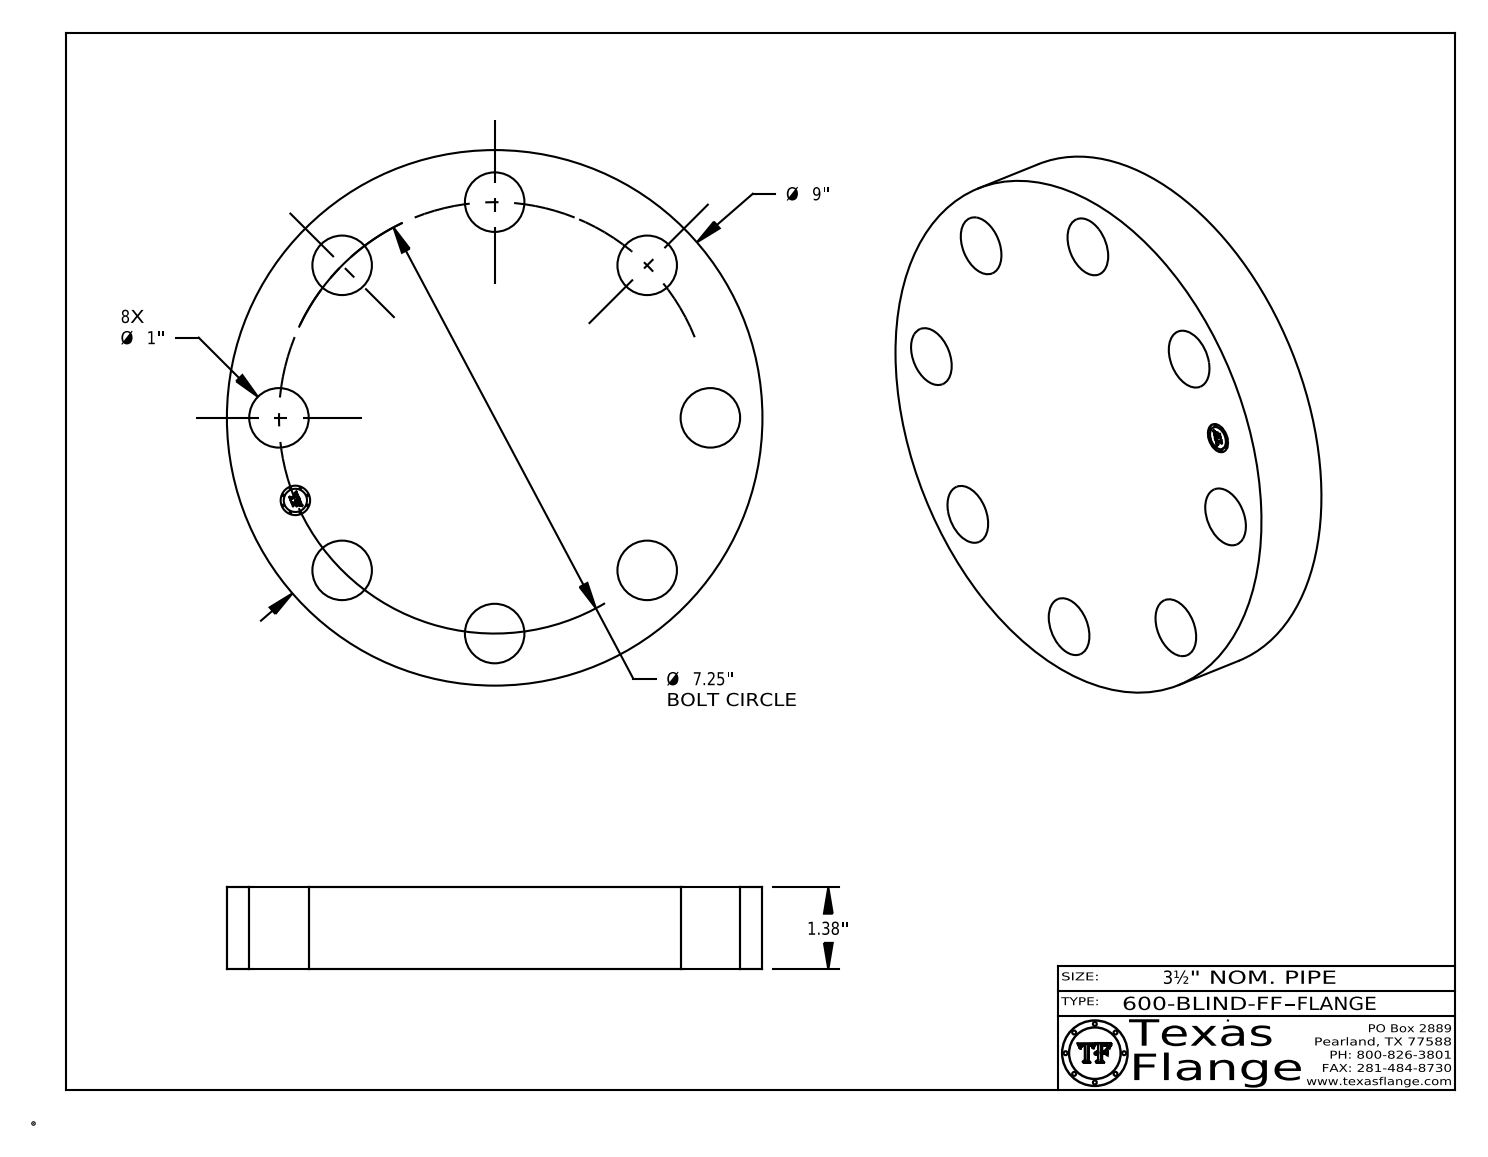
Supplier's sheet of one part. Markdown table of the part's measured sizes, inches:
| quantity | value |
| --- | --- |
| part name | 600-BLIND-FF |
| STEP written by | CATIA V5 STEP AP214 (AUTOMOTIVE_DESIGN) |
| units | inches |
| bodies | 1 solid, 405 faces (367 planar, 38 cylindrical, 0 other) |
| overall size | 9 × 9 × 1.38 |
| volume | 79.12 in³ |
| surface area | 188.5 in² |
| round holes (diameter × count) | 1 × 8, 0.495 × 1 |
| round bosses / shafts (diameter × count) | 0.03 × 8, 9 × 1, 0.39 × 1 |
| main face-to-face distances | 1.38, 1.365, 0.015, 0.148, 0.144, 0.027, 0.096, 0.122, 0.022, 0.101 |
| hole center spacings | 2.774, 5.127, 6.698, 7.25, 1.415, 7.111, 4.028, 4.028 |
